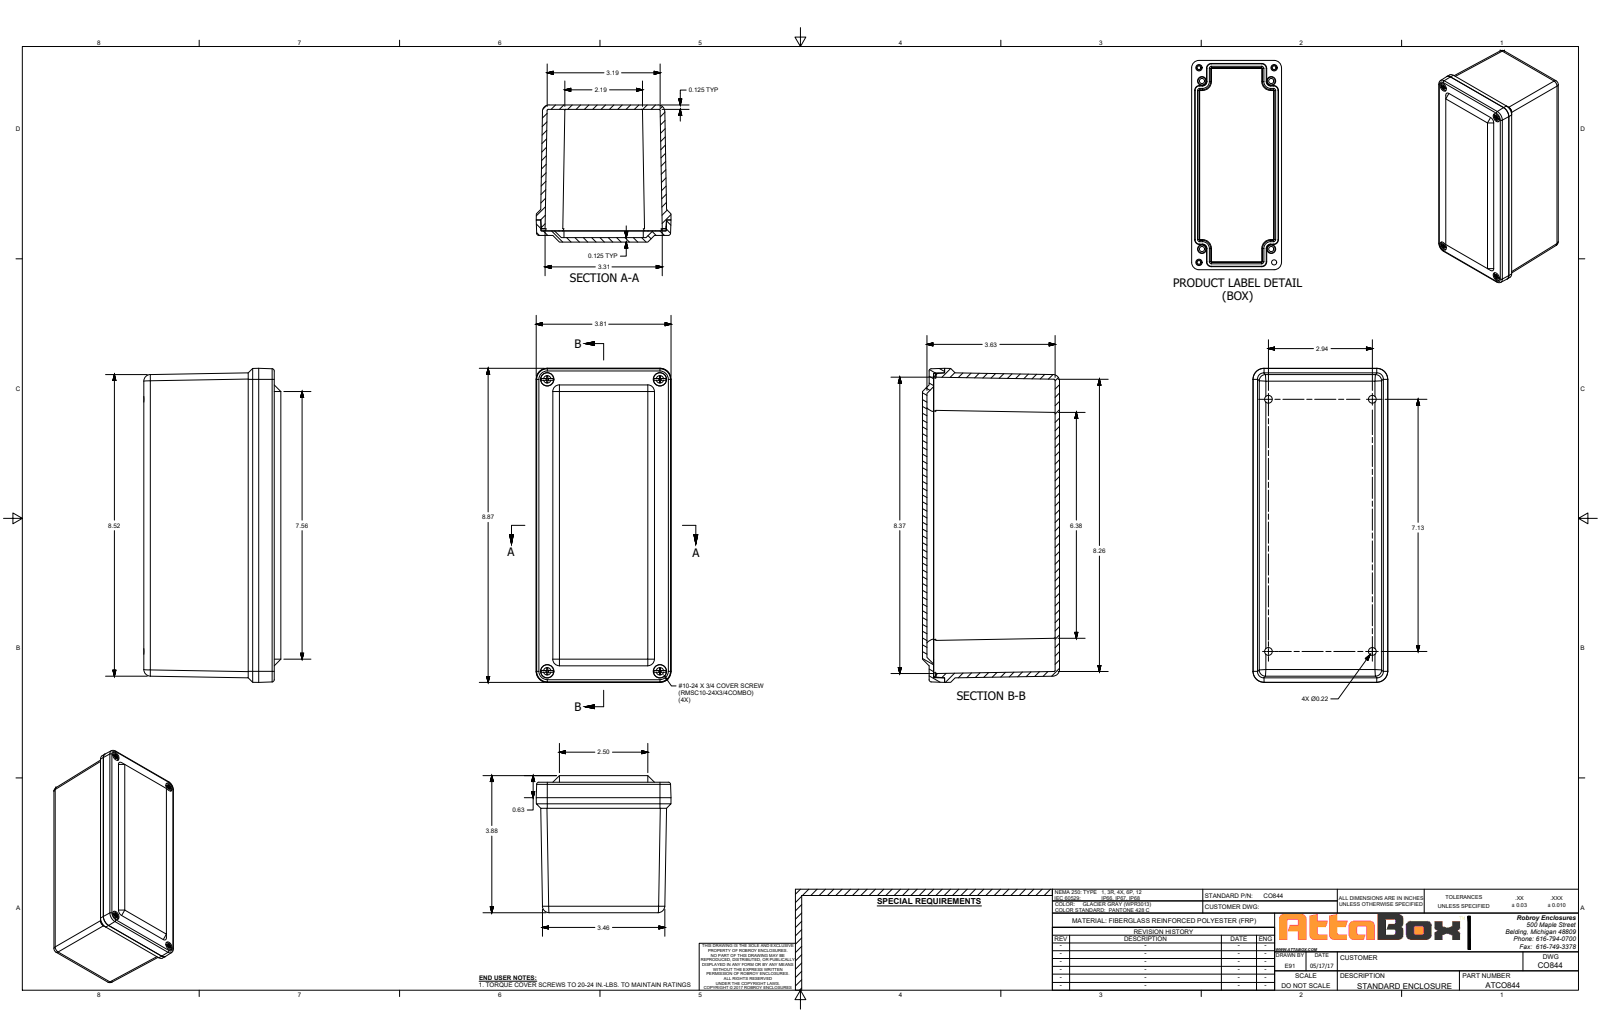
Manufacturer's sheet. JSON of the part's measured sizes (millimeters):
{"part_name": "CO844", "step_written_by": "SolidWorks 2018 (AUTOMOTIVE_DESIGN)", "units": "millimeters", "bodies": {"solids": 11, "faces": 379, "planar": 183, "cylindrical": 100, "other": 96}, "overall_size": [225.4, 98.4, 96.8], "volume_mm3": 405400, "surface_area_mm2": 217600, "round_holes": [[5.6, 8], [4, 4], [4.8, 4], [9.5, 4]], "round_bosses_or_shafts": [[9.4, 4], [6.9, 4], [4.5, 4]], "partial_cylinders_radius": [[0.8, 20], [0.3, 16], [4.5, 4], [4.8, 4], [5.6, 4], [8, 4], [8.3, 4], [1.6, 2]], "face_to_face_distances": [3.3, 3.2, 3.2, 98.4, 95.3, 95.3, 92.1, 90.5, 12.7, 8], "hole_center_spacings": [14.6, 79.1, 195.3, 210.2, 74.6, 80.9, 181, 195.8]}
